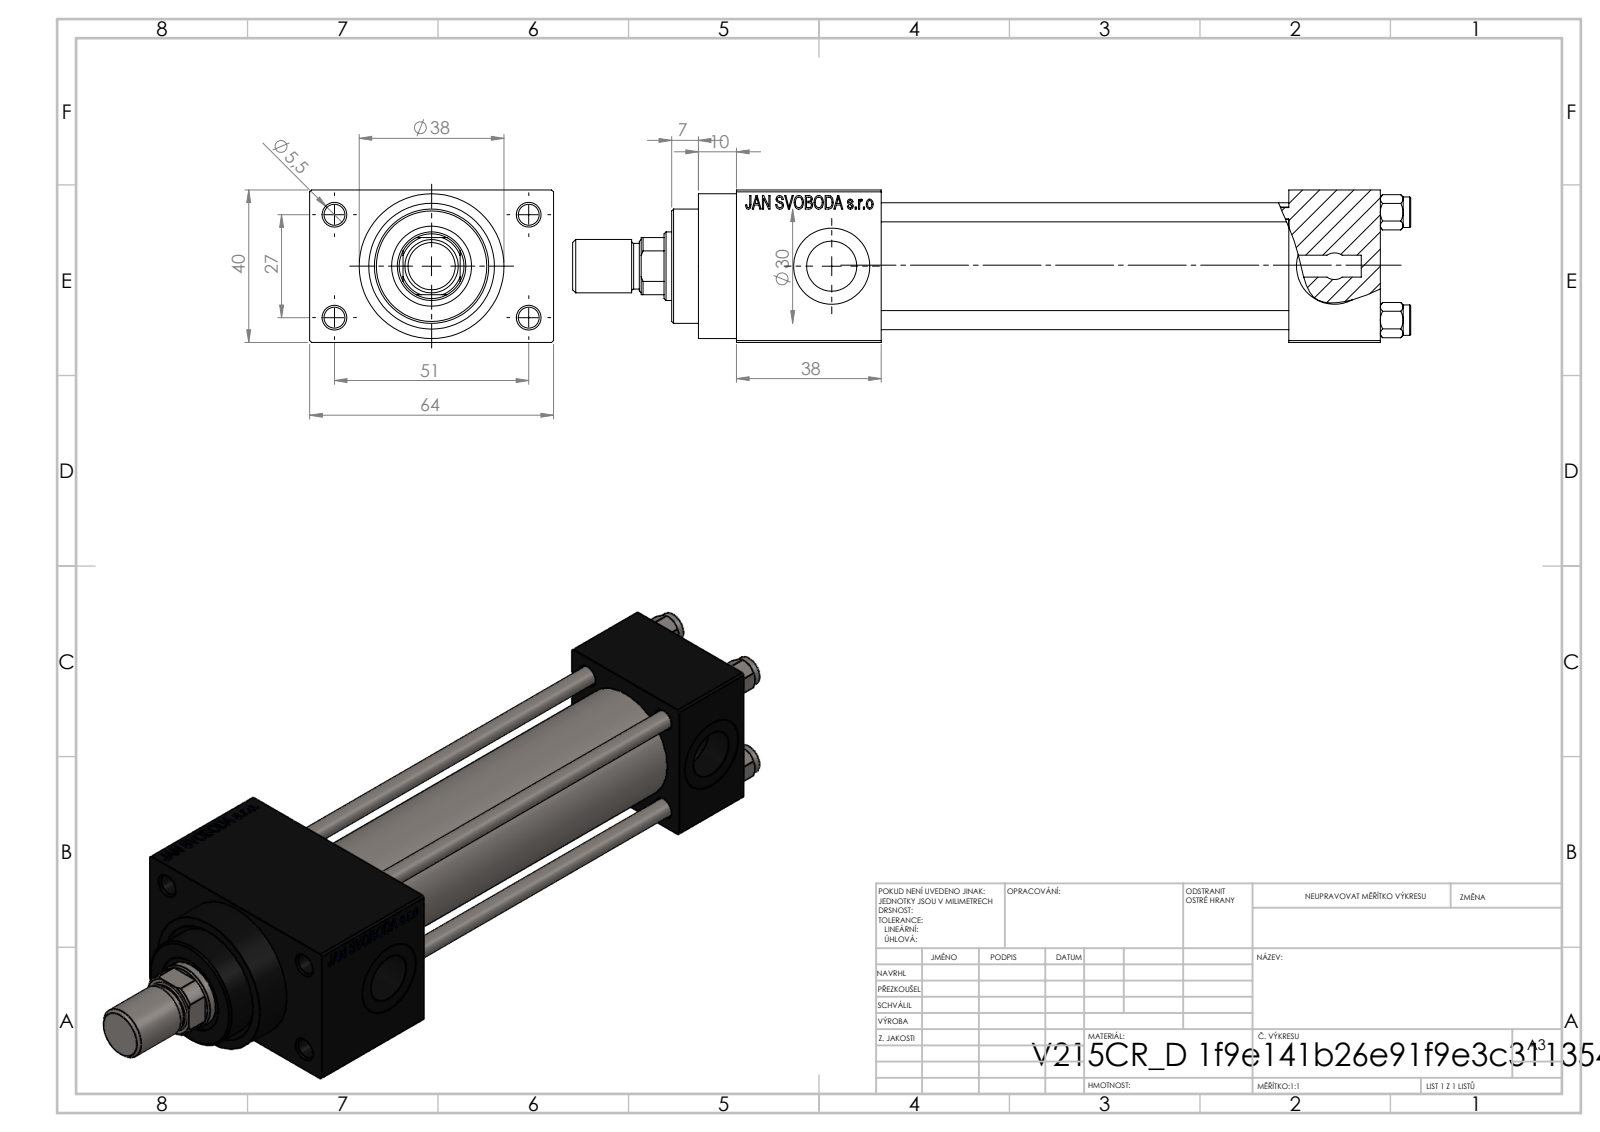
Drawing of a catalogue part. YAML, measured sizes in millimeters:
part_name: "ROD_END_AH; V215CR_D_TYCINKA; V215CR_D_Body; V215CR_VCP_D (+2 more)"
step_written_by: "SolidWorks 2019 (CONFIG_CONTROL_DESIGN)"
units: millimeters
bodies: {solids: 12, faces: 1115, planar: 499, cylindrical: 90, other: 526}
overall_size: [220, 64, 40]
volume: 217860
surface_area: 83409
round_holes:
  - {diameter: 5, count: 4}
  - {diameter: 5.5, count: 4}
  - {diameter: 20, count: 3}
  - {diameter: 7, count: 2}
  - {diameter: 13.16, count: 2}
  - {diameter: 8.5, count: 1}
  - {diameter: 18, count: 1}
  - {diameter: 21, count: 1}
  - {diameter: 25, count: 1}
  - {diameter: 30, count: 1}
round_bosses_or_shafts:
  - {diameter: 8, count: 4}
  - {diameter: 38, count: 1}
  - {diameter: 31, count: 1}
  - {diameter: 14, count: 1}
  - {diameter: 12, count: 1}
partial_cylinders:
  - {radius: 8.5, count: 1}
face_to_face_distances: [40, 12, 107, 24, 131, 52, 38, 169, 145, 64]
hole_center_spacings: [11.37, 20.01, 28.3, 28.85, 29.89, 39.66, 48.34, 27]
